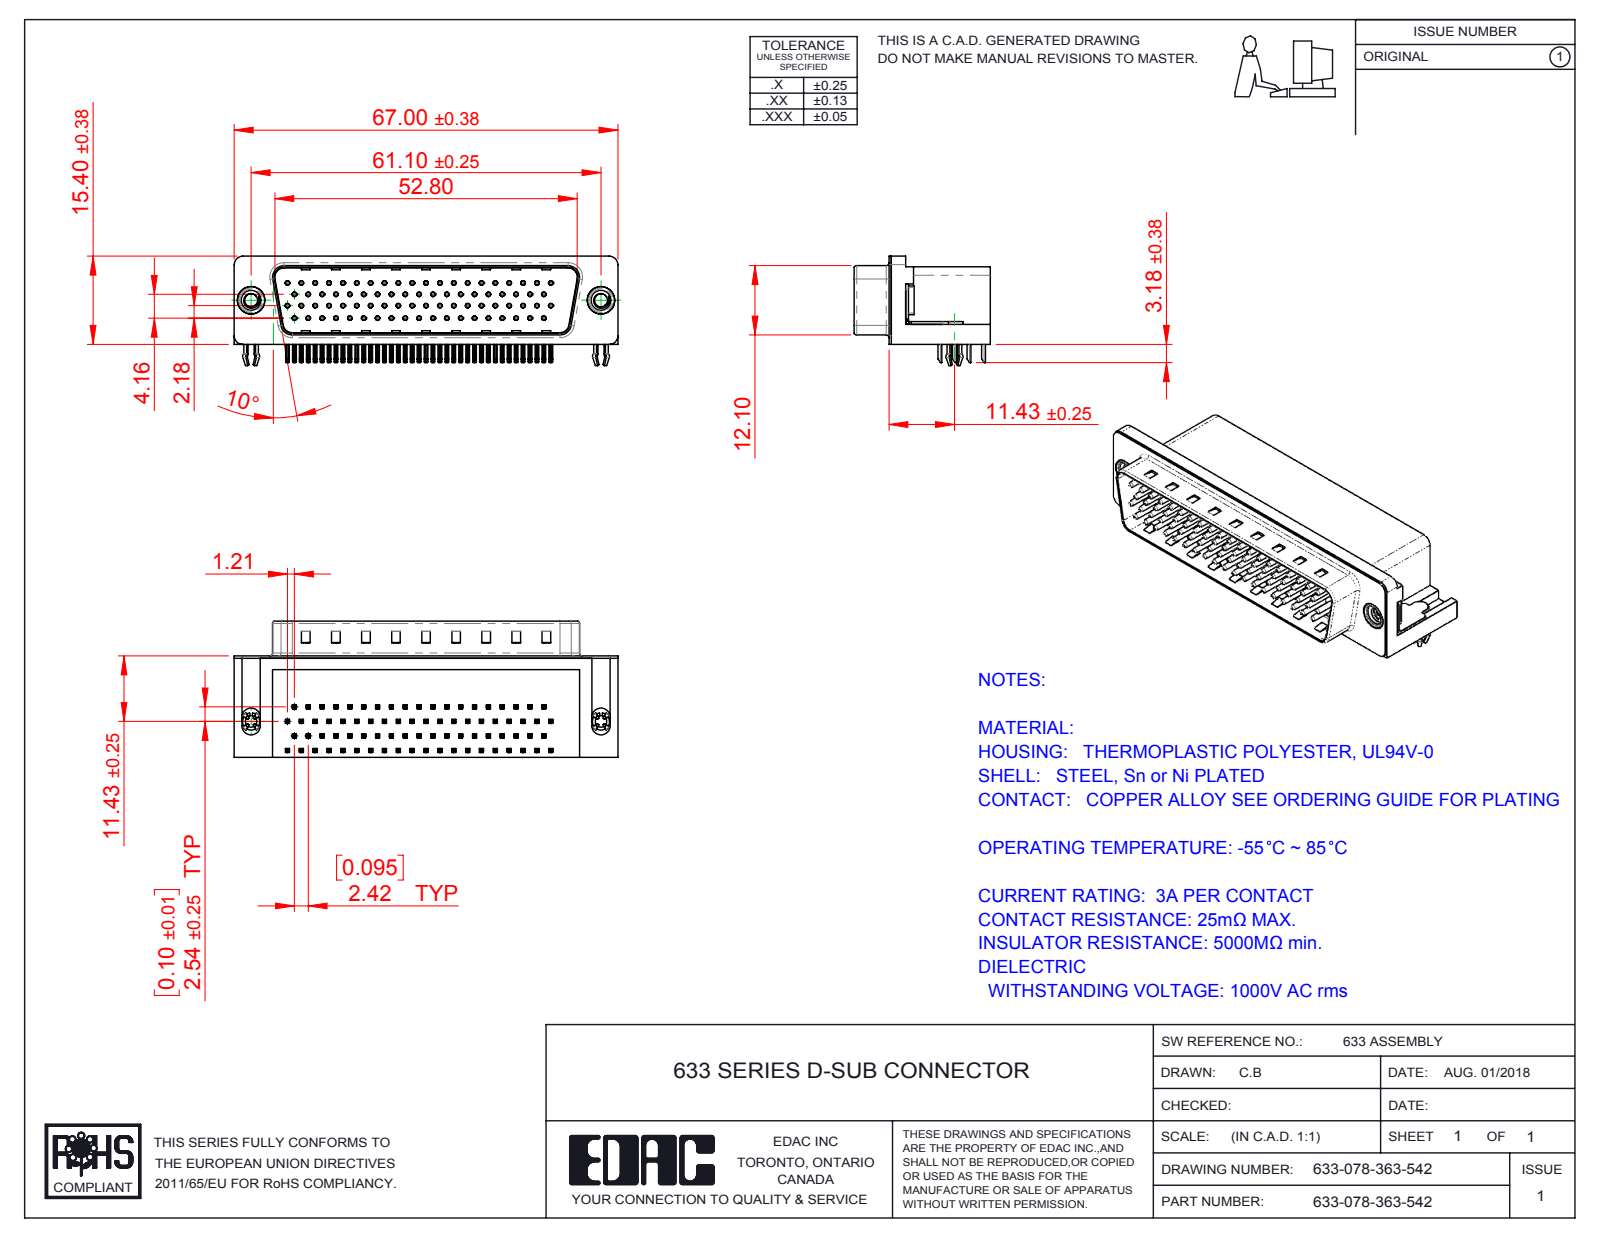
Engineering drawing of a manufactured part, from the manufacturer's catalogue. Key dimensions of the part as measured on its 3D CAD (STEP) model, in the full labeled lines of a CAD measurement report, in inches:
Part name (STEP PRODUCT): 633-078-363-542; 633 Housing_78 Contact; 633 Shell_78 Contact; 633 Contact Bottom_78 Contact (+5 more)
STEP written by: SolidWorks 2016 (CONFIG_CONTROL_DESIGN)
Units: inches
Bodies: 84 solids, 6396 faces (4023 planar, 1784 cylindrical, 589 other)
Overall size (bounding box): 2.638 × 0.937 × 0.752
Volume: 0.892 in³ · Surface area: 25.47 in²
Round holes (diameter × count): ⌀0.014 ×78, ⌀0.031 ×78, ⌀0.079 ×2, ⌀0.089 ×2, ⌀0.157 ×2, ⌀0.189 ×2, ⌀0.197 ×2
Round bosses / shafts (diameter × count): ⌀0.03 ×78, ⌀0.193 ×2, ⌀0.187 ×2, ⌀0.154 ×2, ⌀0.118 ×2
Partial cylindrical surfaces — rounded edges, fillets, slot ends (radius × count): R0.01 ×324, R0.005 ×156, R0.039 ×16, R0.02 ×9, R0.063 ×8, R0.059 ×6, R0.018 ×4, R0.035 ×4
Main face-to-face distances: 0.016, 0.52, 0.681, 0.461, 0.526, 0.081, 0.541, 0.065, 0.073, 0.469
Hole centre spacings: 0.095, 0.191, 0.286, 0.381, 0.246, 0.281, 0.476, 0.339
